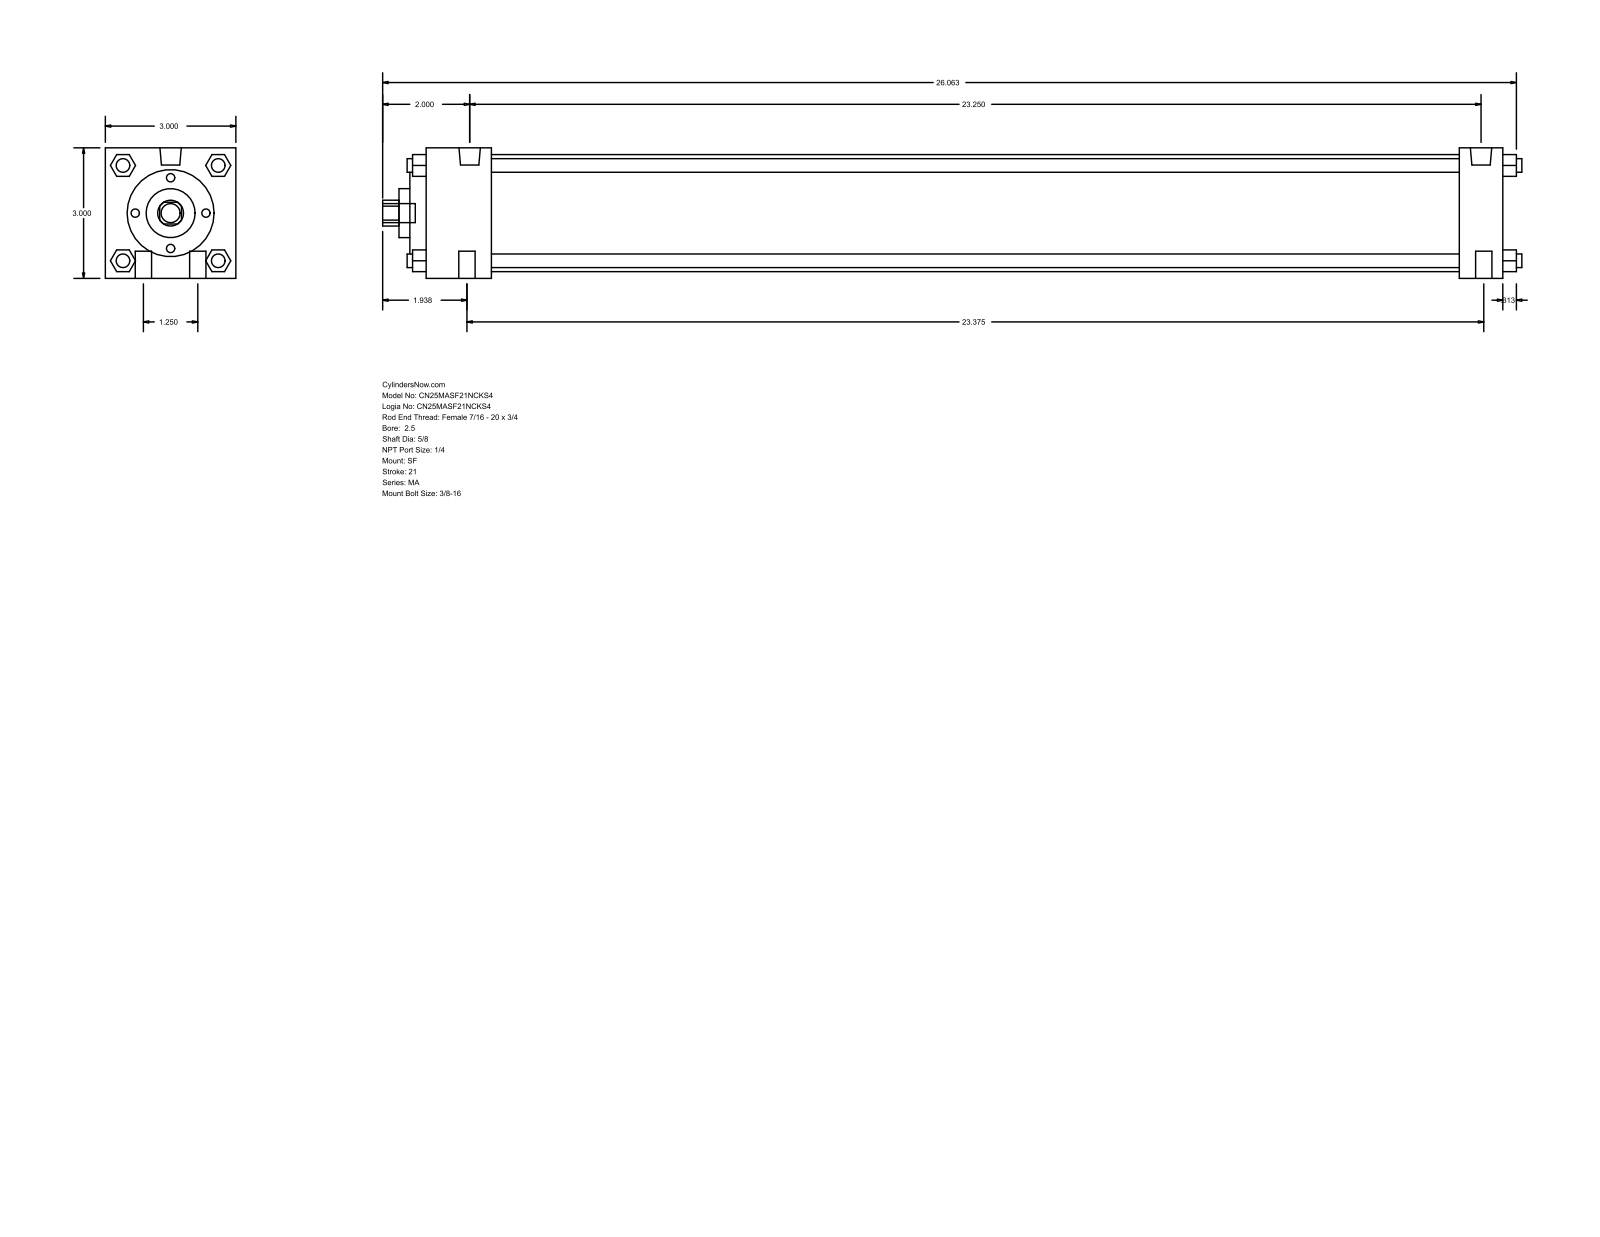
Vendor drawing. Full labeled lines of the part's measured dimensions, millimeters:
Part name (STEP PRODUCT): MA_SF__0250_0.625
STEP written by: GSSL Pune (CONFIG_CONTROL_DESIGN)
Units: millimetres
Bodies: 0 solids, 126 faces (95 planar, 31 cylindrical, 0 other)
Overall size (bounding box): 665.16 × 76.2 × 76.2
Round holes (diameter × count): ⌀15.88 ×1, ⌀28.57 ×1, ⌀50.8 ×1, ⌀68.33 ×1
Round bosses / shafts (diameter × count): ⌀7.94 ×6, ⌀9.53 ×4, ⌀12.49 ×2, ⌀11.11 ×1
Partial cylindrical surfaces — rounded edges, fillets, slot ends (radius × count): R7.54 ×1
Main face-to-face distances: 76.2, 628.65, 25.4, 603.25, 38.1, 565.15, 590.55, 12.7, 9.52, 47.62
